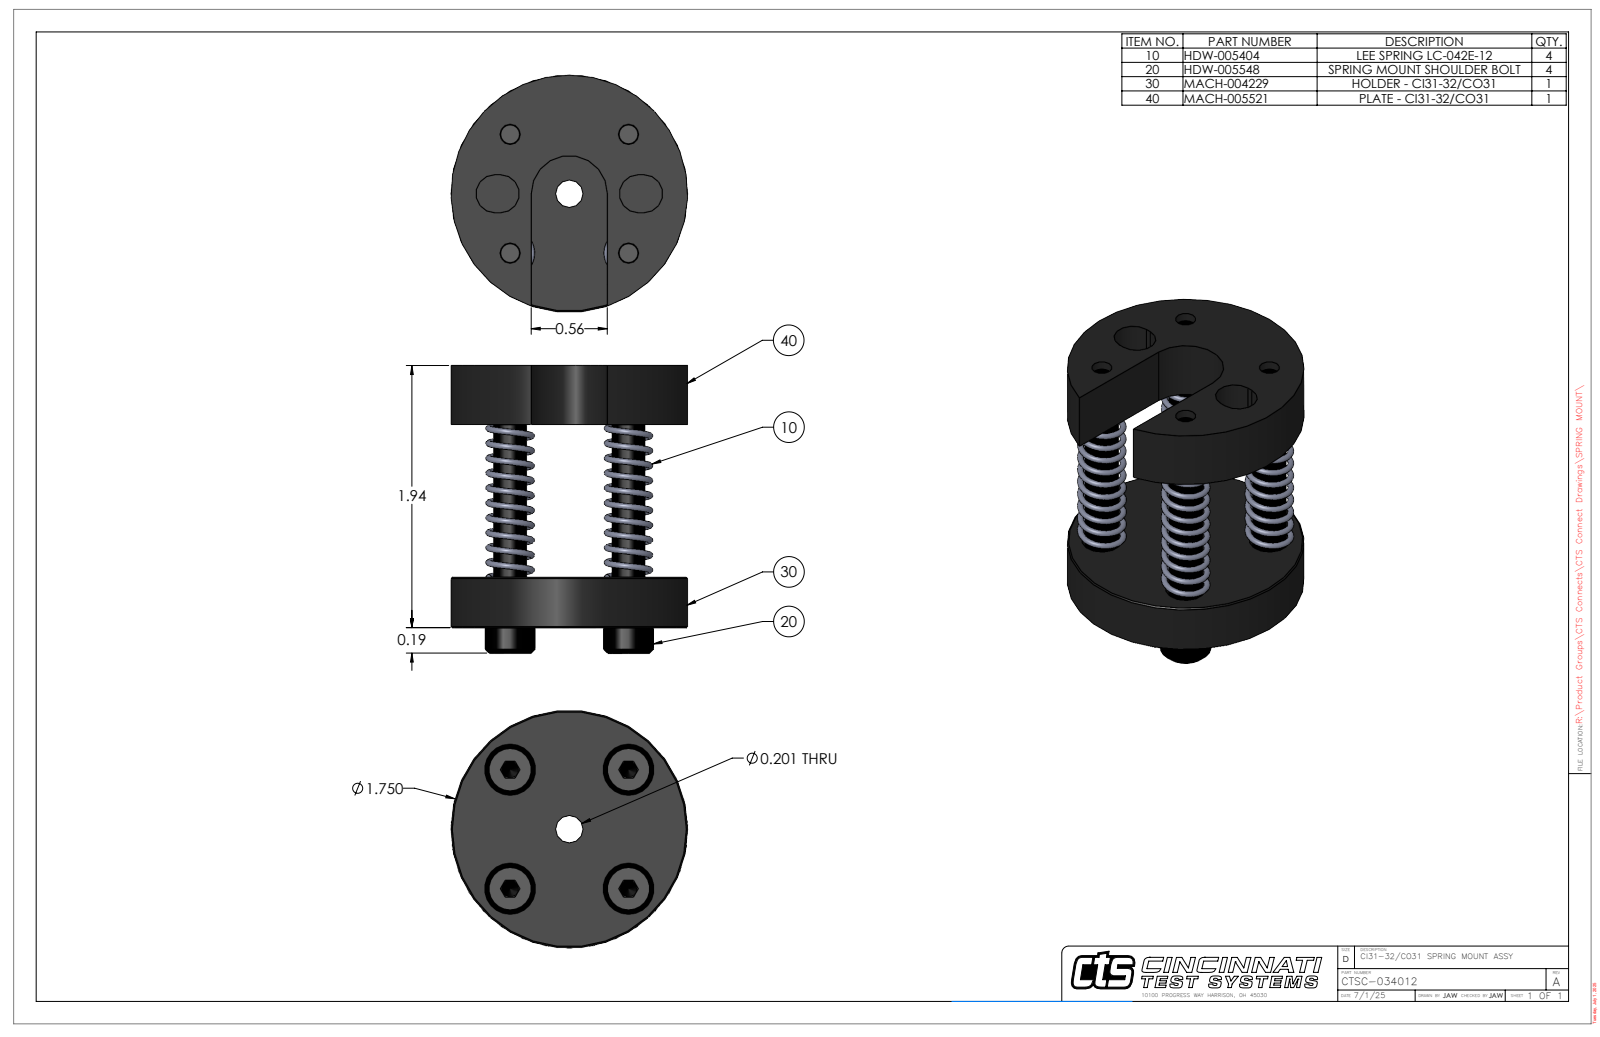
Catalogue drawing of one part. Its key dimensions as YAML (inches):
part_name: "MACH-005521 (PLATE - CI31-32,CO31); CTSC-034012 (CI31-32, CO31 SPRING MOUNT); MACH-004229 (HOLDER - CI31-2,CO31 REV1); HDW-005404 (LEE SPRING LC-042E-12) (+1 more)"
step_written_by: "SolidWorks 2023 (AUTOMOTIVE_DESIGN)"
units: inches
bodies: {solids: 10, faces: 228, planar: 90, cylindrical: 70, other: 68}
overall_size: [2.126, 1.75, 1.75]
volume: 1.933
surface_area: 28.73
round_holes:
  - {diameter: 0.15, count: 4}
  - {diameter: 0.297, count: 4}
  - {diameter: 0.201, count: 1}
round_bosses_or_shafts:
  - {diameter: 0.375, count: 4}
  - {diameter: 0.248, count: 4}
  - {diameter: 0.227, count: 4}
  - {diameter: 0.19, count: 4}
  - {diameter: 0.133, count: 4}
  - {diameter: 1.75, count: 1}
partial_cylinders:
  - {radius: 0.141, count: 4}
  - {radius: 0.281, count: 1}
face_to_face_distances: [0.375, 1.5, 1.125, 0.438, 1.563, 1.938, 0.562, 2.126, 1.688, 0.563]
hole_center_spacings: [0.619, 0.875, 1.237]
